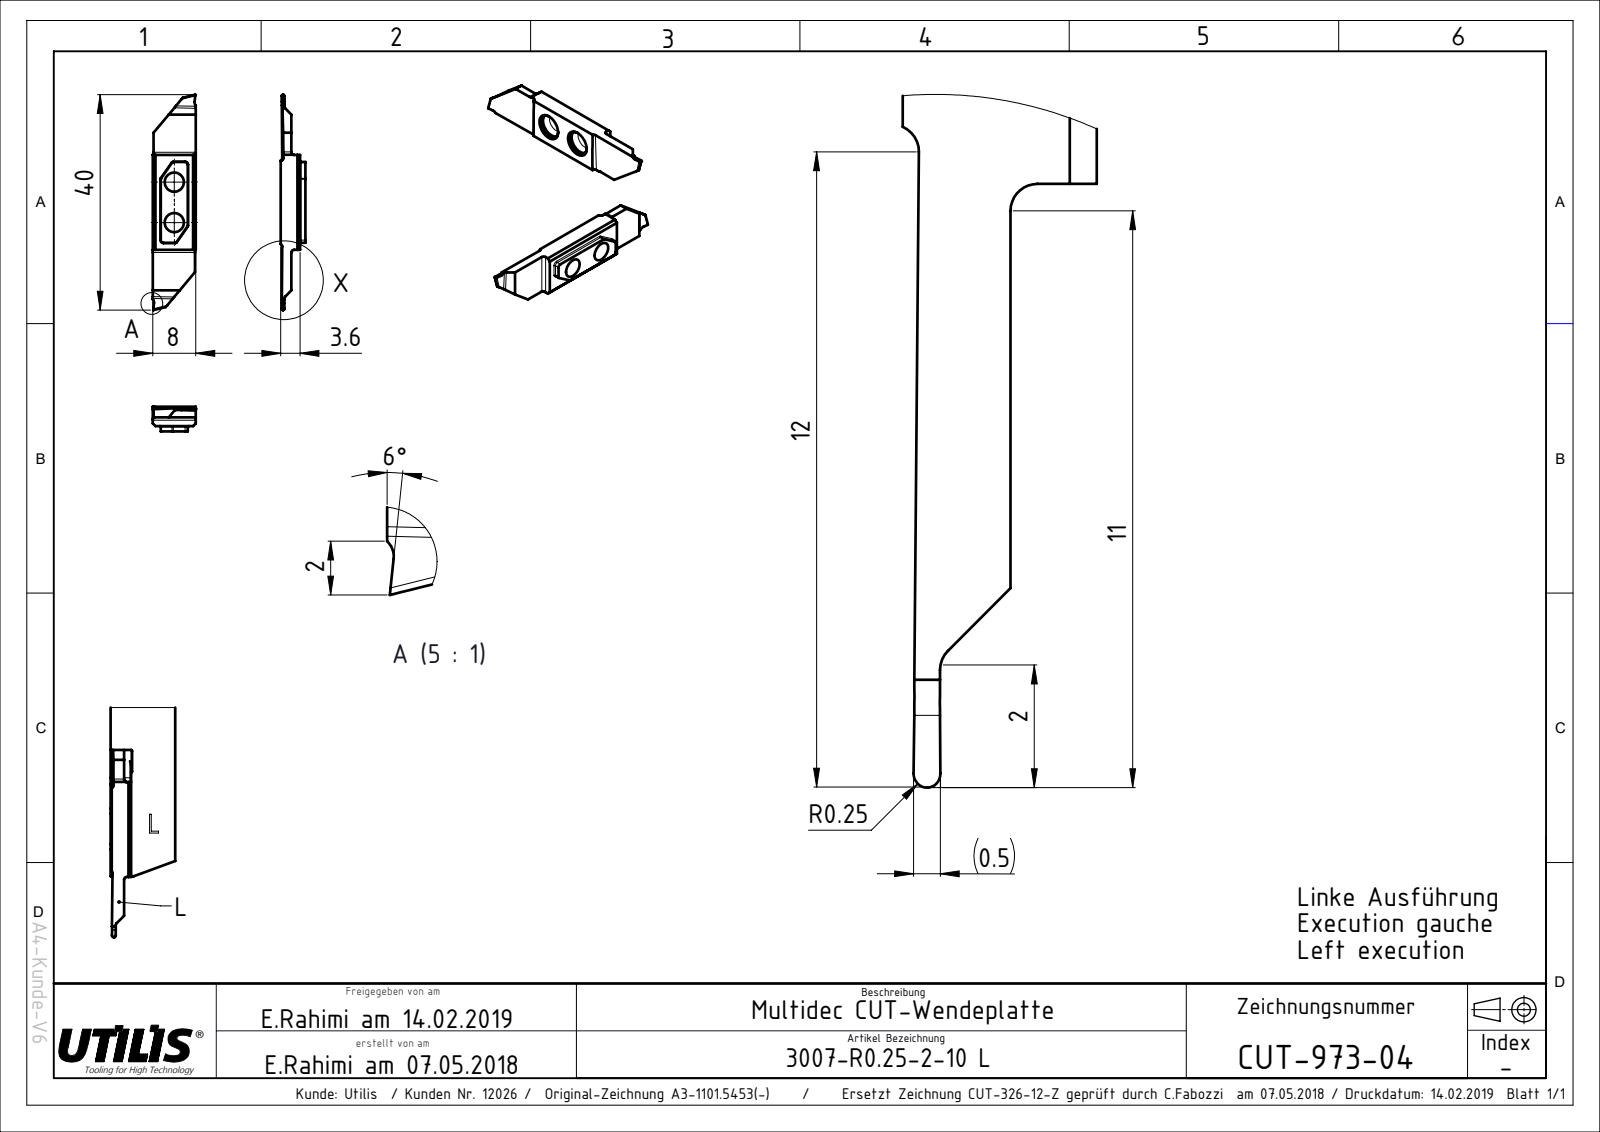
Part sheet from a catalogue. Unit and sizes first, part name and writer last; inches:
Units: inches
Overall size (bounding box): 1.575 × 0.315 × 0.142
Round holes (diameter × count): ⌀0.14 ×2
Partial cylindrical surfaces — rounded edges, fillets, slot ends (radius × count): R0.02 ×6, R0.01 ×2, R0.031 ×2, R0.039 ×2
Main face-to-face distances: 0.142, 0.079, 0.063, 0.315, 0.309, 0.887, 0.693, 0.303, 0.298, 0.441
Hole centre spacings: 0.295
Volume: 0.039 in³ · Surface area: 1.24 in²
Bodies: 1 solid, 42 faces (24 planar, 18 cylindrical, 0 other)
Part name (STEP PRODUCT): CUT-973; ASME Y14.5
STEP written by: FormatWorks Professional (AP242_MANAGED_MODEL_BASED_3D_ENGINEERING_MIM_LF)
